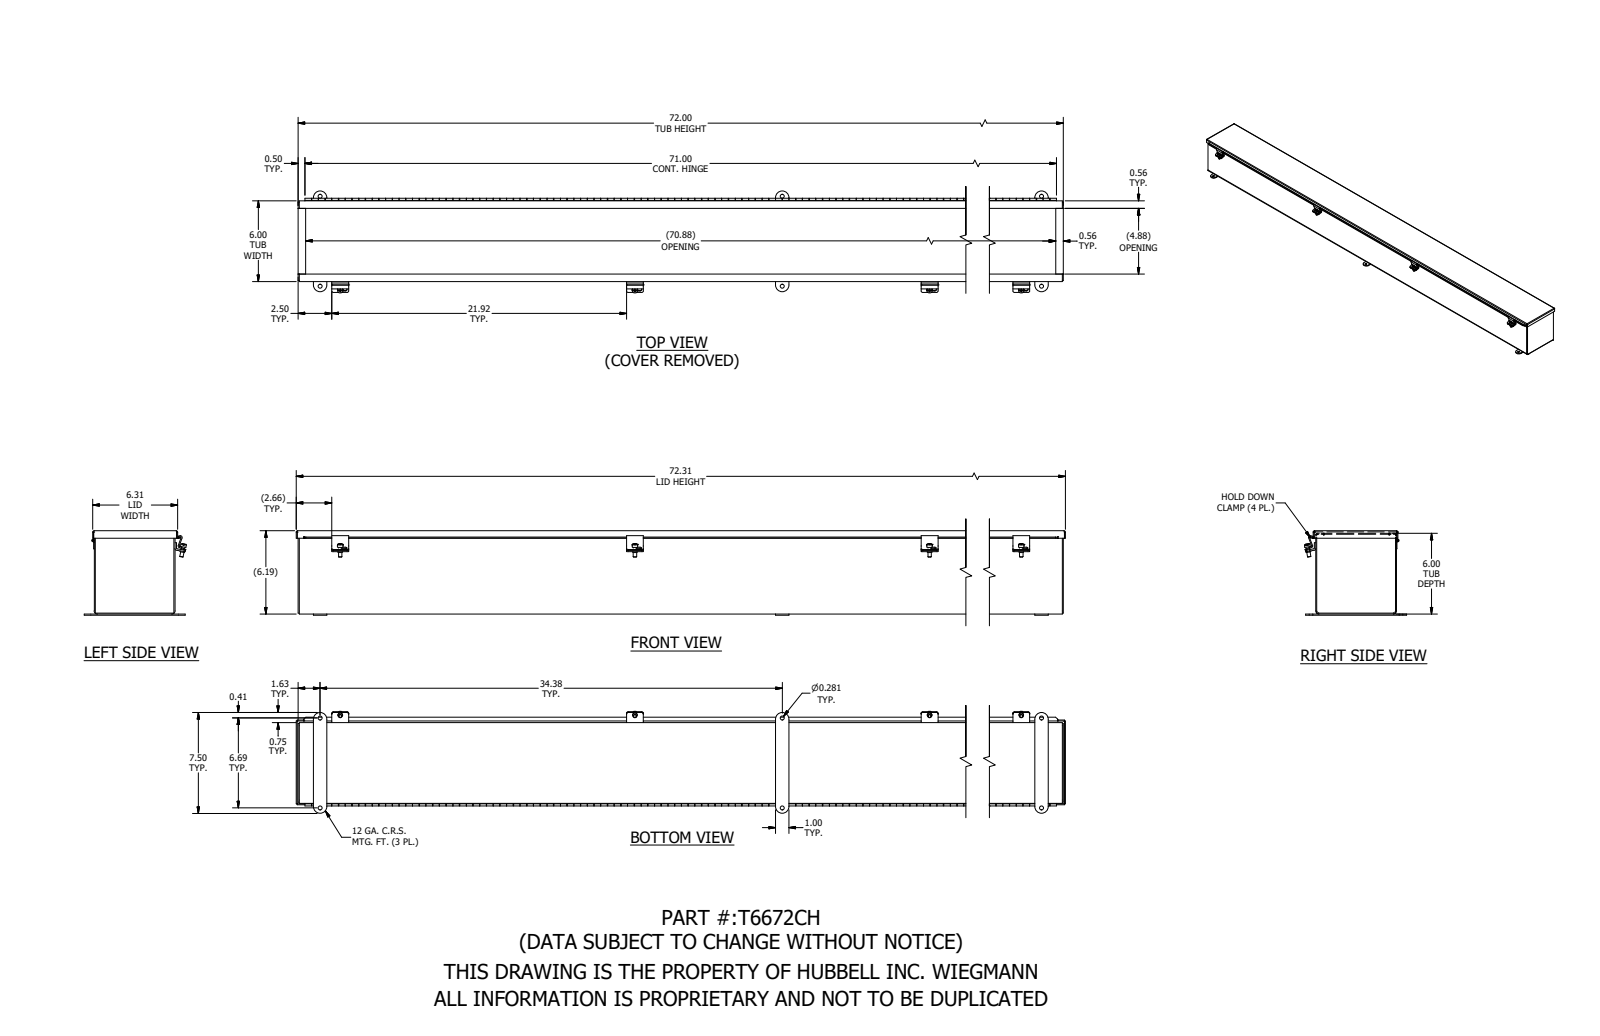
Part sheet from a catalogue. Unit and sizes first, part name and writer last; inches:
Units: inches
Overall size (bounding box): 72.313 × 7.595 × 6.283
Round holes (diameter × count): ⌀0.281 ×6, ⌀0.196 ×4, ⌀0.116 ×1
Round bosses / shafts (diameter × count): ⌀0.41 ×4, ⌀0.344 ×4, ⌀0.25 ×4, ⌀0.2 ×1, ⌀0.1 ×1
Partial cylindrical surfaces — rounded edges, fillets, slot ends (radius × count): R0.125 ×16, R0.031 ×9, R0.105 ×9, R0.133 ×8, R0.5 ×6, R0.063 ×3, R0.126 ×3, R0.156 ×2
Main face-to-face distances: 0.074, 5.926, 6.115, 6, 5.852, 6.189, 6.041, 0.189, 0.116, 6.042
Hole centre spacings: 6.687, 21.917, 34.375, 34.375, 35.019, 35.02, 68.75, 69.074
Volume: 152.8 in³ · Surface area: 4 263 in²
Bodies: 22 solids, 1389 faces (664 planar, 697 cylindrical, 28 other)
Part name (STEP PRODUCT): T6672CH
STEP written by: SolidWorks 2021 (AUTOMOTIVE_DESIGN)
